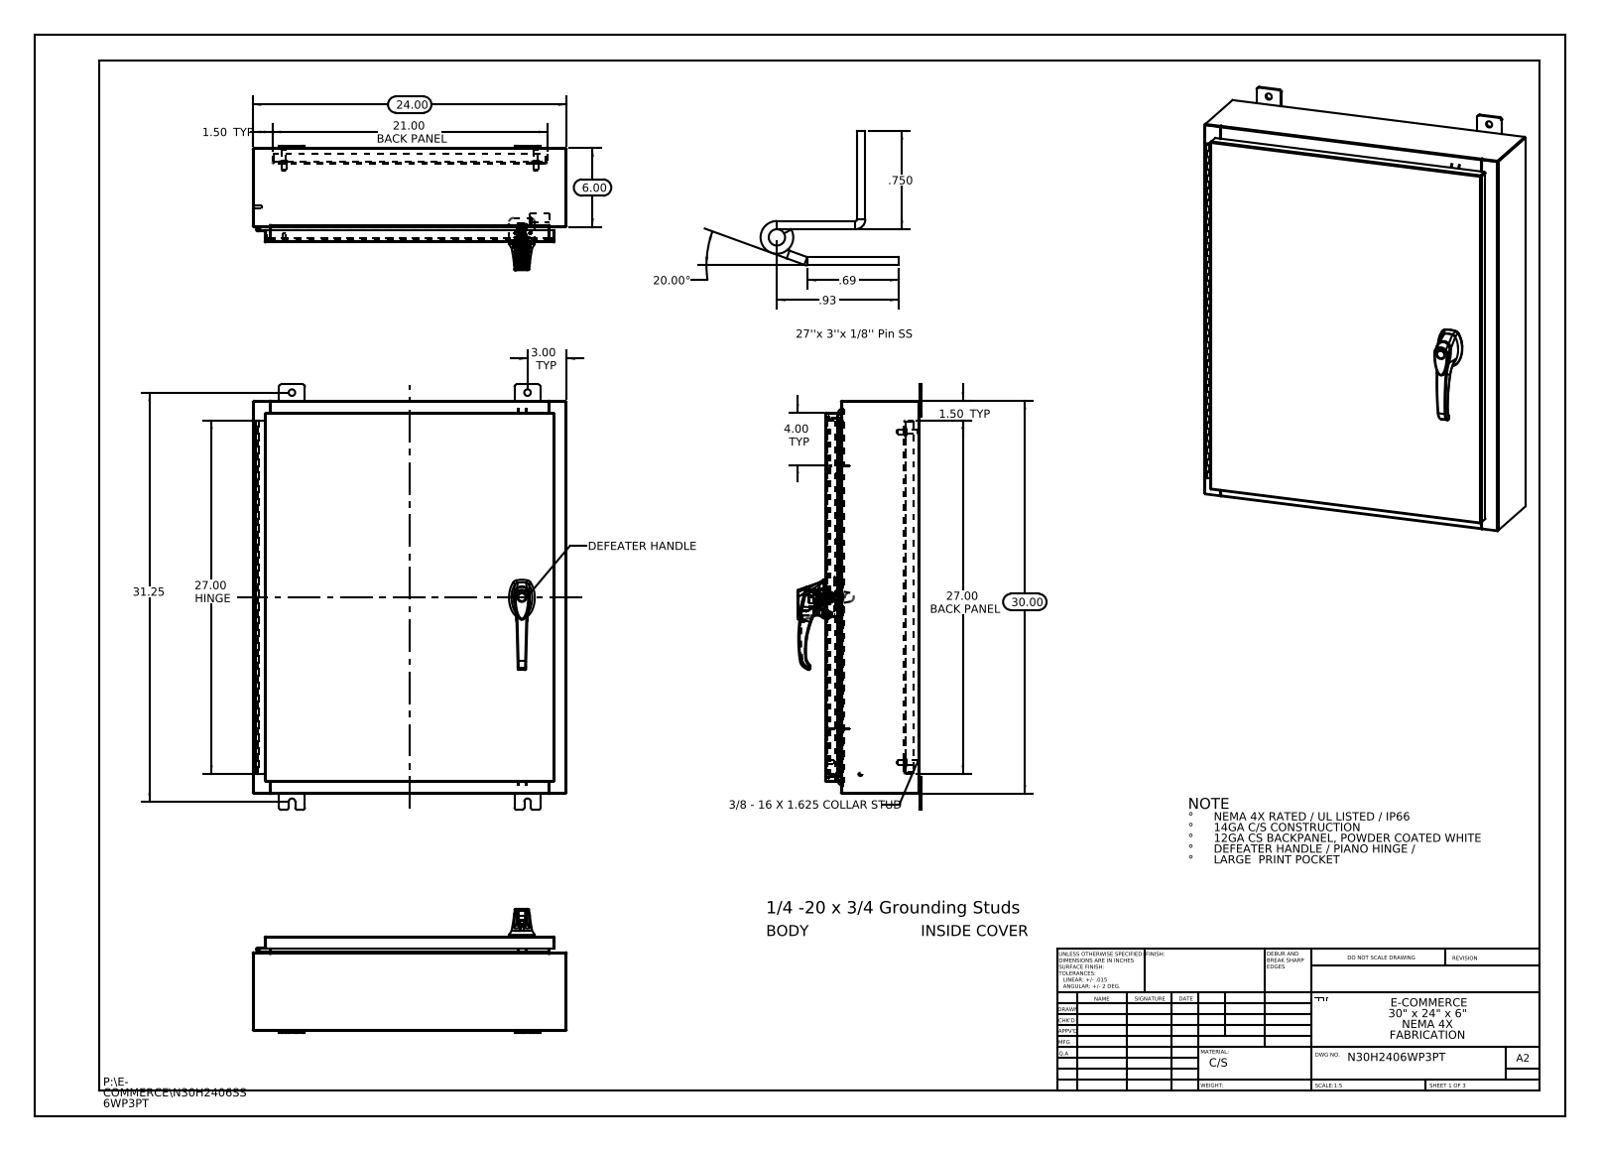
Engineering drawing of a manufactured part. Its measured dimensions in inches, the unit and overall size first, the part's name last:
Units: inches
Overall size (bounding box): 32.5 × 24 × 9.495
Round holes (diameter × count): ⌀0.5 ×8, ⌀0.25 ×4, ⌀0.138 ×3, ⌀0.161 ×3, ⌀0.079 ×2, ⌀0.203 ×2, ⌀0.313 ×2, ⌀0.437 ×2, ⌀0.125 ×1, ⌀0.125 ×1, ⌀0.197 ×1, ⌀0.276 ×1
Round bosses / shafts (diameter × count): ⌀0.625 ×4, ⌀0.375 ×4, ⌀0.33 ×4, ⌀0.157 ×4, ⌀0.14 ×4, ⌀0.315 ×3, ⌀0.236 ×3, ⌀1.181 ×1
Partial cylindrical surfaces — rounded edges, fillets, slot ends (radius × count): R0.118 ×37, R0.006 ×33, R0.013 ×24, R0.19 ×24, R0.088 ×18, R0.039 ×15, R0.028 ×12, R0.008 ×6
Main face-to-face distances: 0.075, 7.126, 0.104, 7.051, 7.201, 1, 1.075, 6.051, 6.126, 1.179
Hole centre spacings: 8.369, 0.295, 0.625, 0.841, 1.25, 1.313, 1.561, 1.858
Volume: 256.1 in³ · Surface area: 6 284 in²
Bodies: 37 solids, 2662 faces (971 planar, 993 cylindrical, 698 other)
Part name (STEP PRODUCT): 26161102; Quarter-20 CD Stud; 10_30 CD Stud; N30H2406SS6WP3PT (+8 more)
STEP written by: SolidWorks 2013 (CONFIG_CONTROL_DESIGN)
